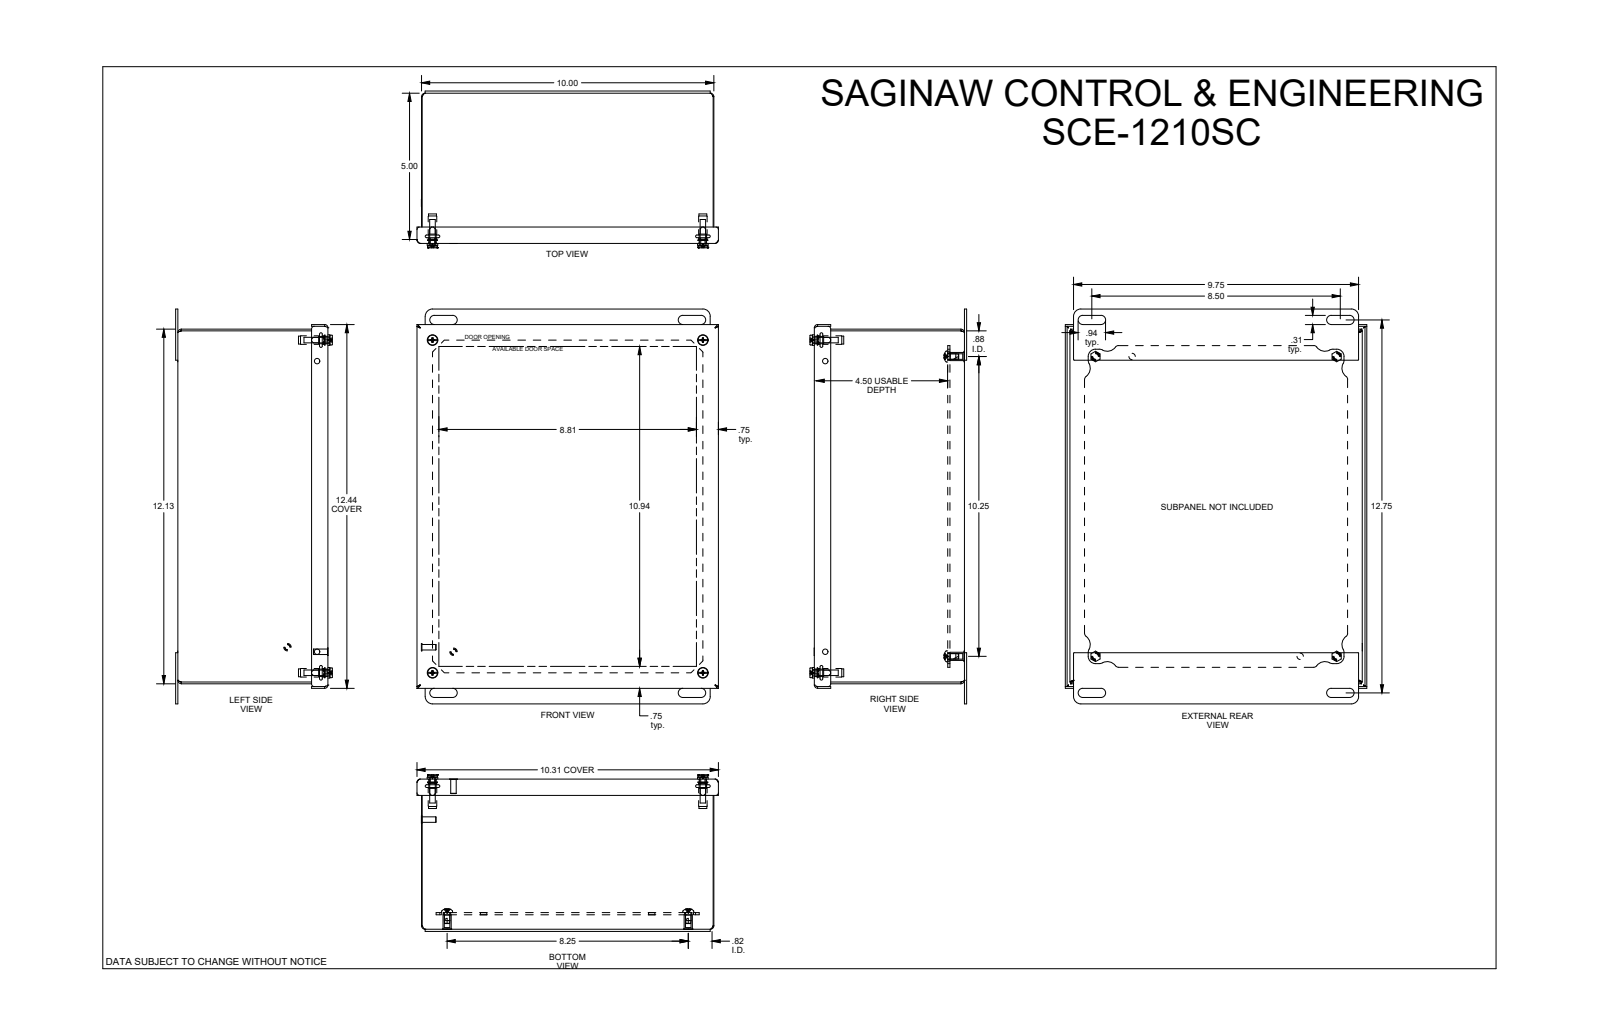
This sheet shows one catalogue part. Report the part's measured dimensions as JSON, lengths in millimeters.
{"part_name": "SCE-1210SC", "step_written_by": "SolidWorks 2019 (AUTOMOTIVE_DESIGN)", "units": "millimeters", "bodies": {"solids": 28, "faces": 805, "planar": 328, "cylindrical": 207, "other": 270}, "overall_size": [342.9, 262, 136.2], "volume_mm3": 676900, "surface_area_mm2": 852300, "round_holes": [[4.8, 8], [6.4, 8], [5.6, 4], [6.8, 4], [7.1, 4], [8.1, 4], [4.7, 2], [5.5, 2], [4.9, 1]], "round_bosses_or_shafts": [[4.8, 10], [11.1, 4], [9.5, 4], [9.2, 4], [8.6, 4], [8.5, 4], [7.4, 4], [7.1, 4]], "partial_cylinders_radius": [[3.2, 16], [6.4, 16], [1.5, 12], [0.1, 8], [1.3, 8], [1.6, 8], [4, 8], [6.5, 8]], "face_to_face_distances": [1.5, 128.9, 130.4, 127.4, 252.5, 114.4, 1.9, 116.3, 14.5, 13], "hole_center_spacings": [274.9, 19.1, 353.3, 222.7, 222.7, 235, 260.4, 288.9]}
